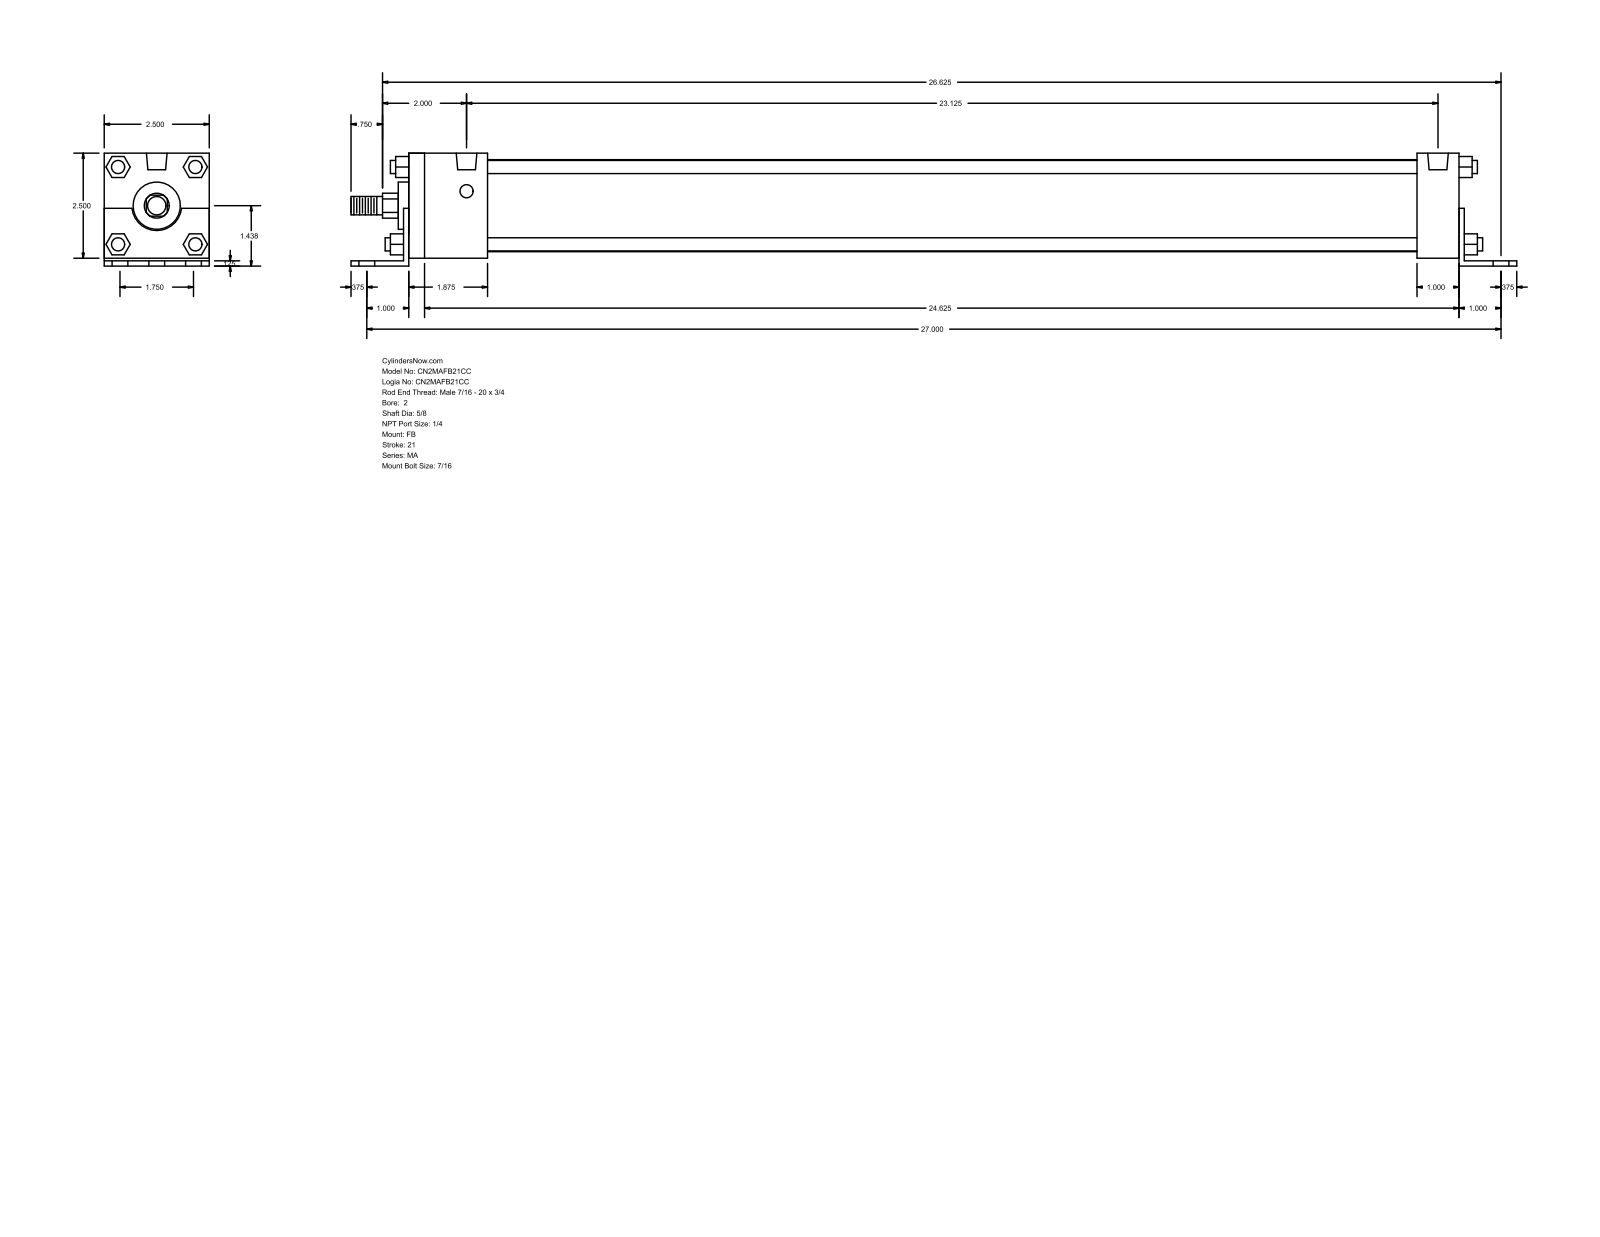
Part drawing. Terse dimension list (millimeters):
name: MA_FB__0200_0.625
written by: GSSL Pune (CONFIG_CONTROL_DESIGN)
unit: mm
bodies: 0 solids, 140 faces (105 planar, 35 cylindrical, 0 other)
size: 704.85 × 68.26 × 63.5
holes: 6× ⌀11.11, 4× ⌀7.94, 2× ⌀12.49
bosses: 4× ⌀7.94, 1× ⌀55.63, 1× ⌀28.57, 1× ⌀15.88, 1× ⌀11.11
rounds: 1× R7.54, 1× R15.05
face distances: 63.5, 3.17, 4.76, 68.26, 1.59, 65.09, 641.35, 3.18, 635, 638.17
hole spacings: 22.23, 686.16, 685.8, 44.11, 44.46, 64.3, 587.37, 625.86
